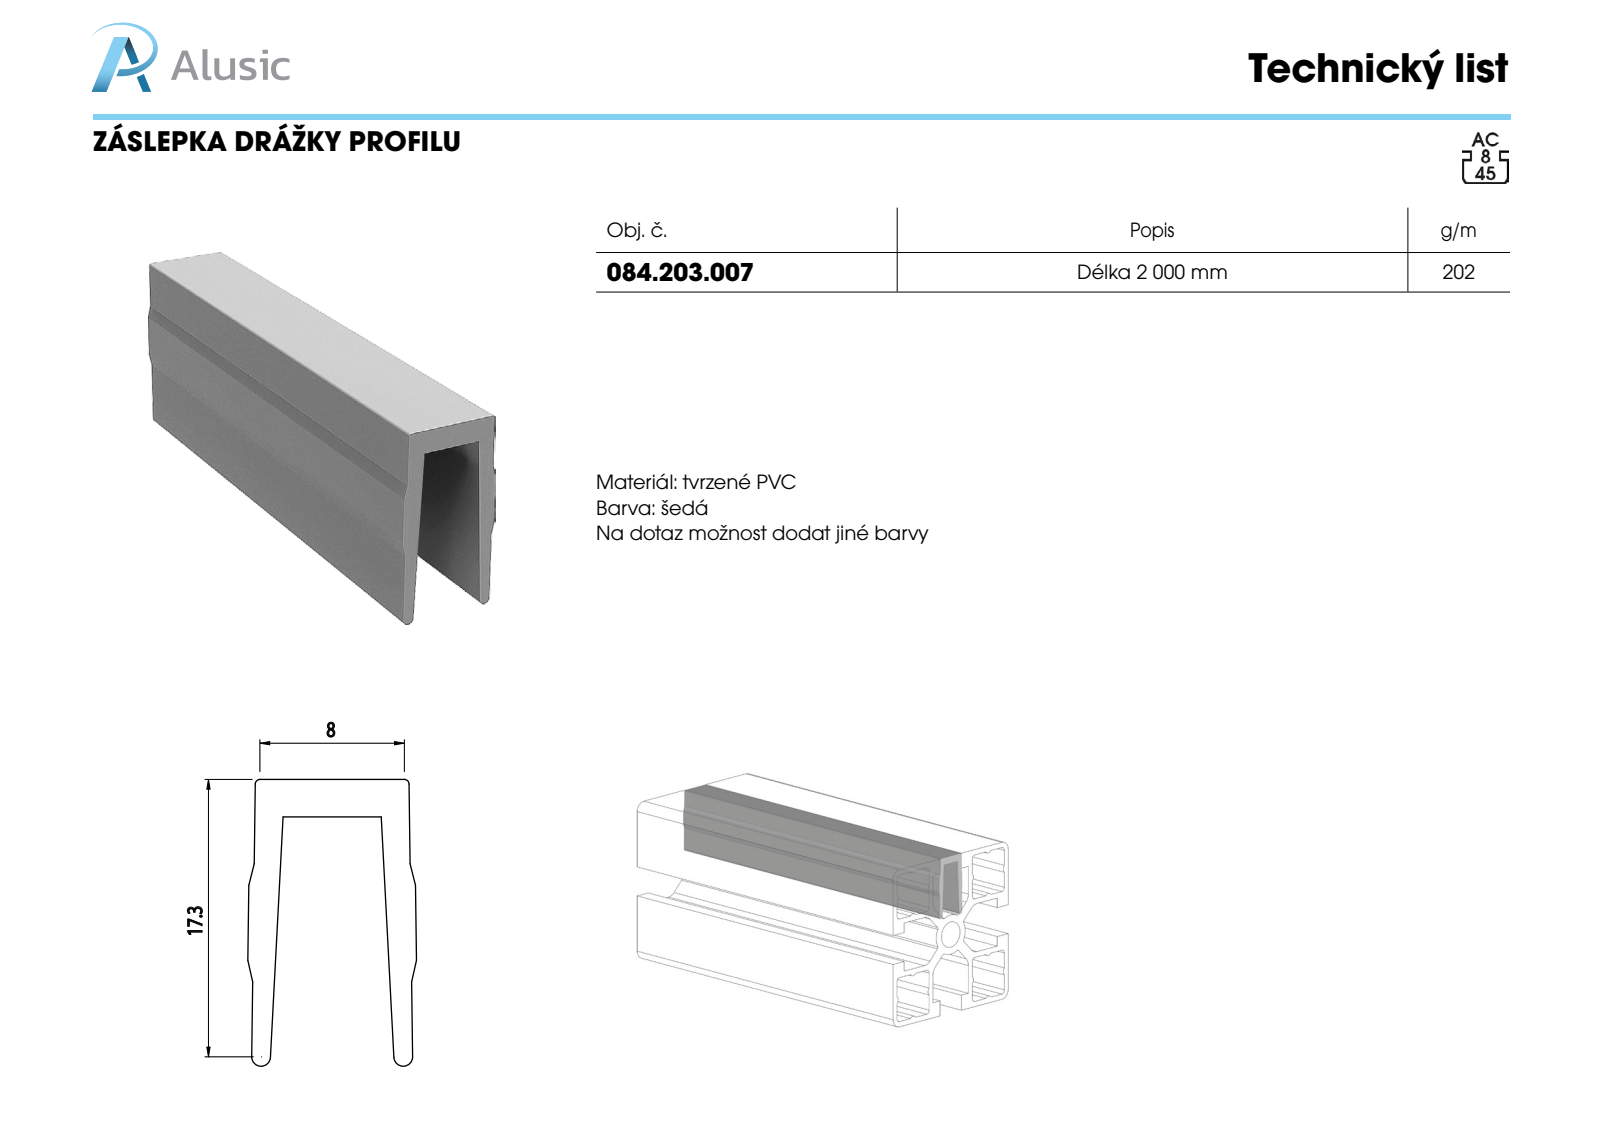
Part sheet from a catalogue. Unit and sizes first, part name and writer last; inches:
Units: inches
Overall size (bounding box): 3.937 × 0.681 × 0.354
Partial cylindrical surfaces — rounded edges, fillets, slot ends (radius × count): R0.01 ×2, R0.02 ×2
Main face-to-face distances: 0.079, 3.937
Volume: 0.35 in³ · Surface area: 12.53 in²
Bodies: 1 solid, 20 faces (16 planar, 4 cylindrical, 0 other)
Part name (STEP PRODUCT): 084.203.007
STEP written by: SolidWorks 2011 (CONFIG_CONTROL_DESIGN)
